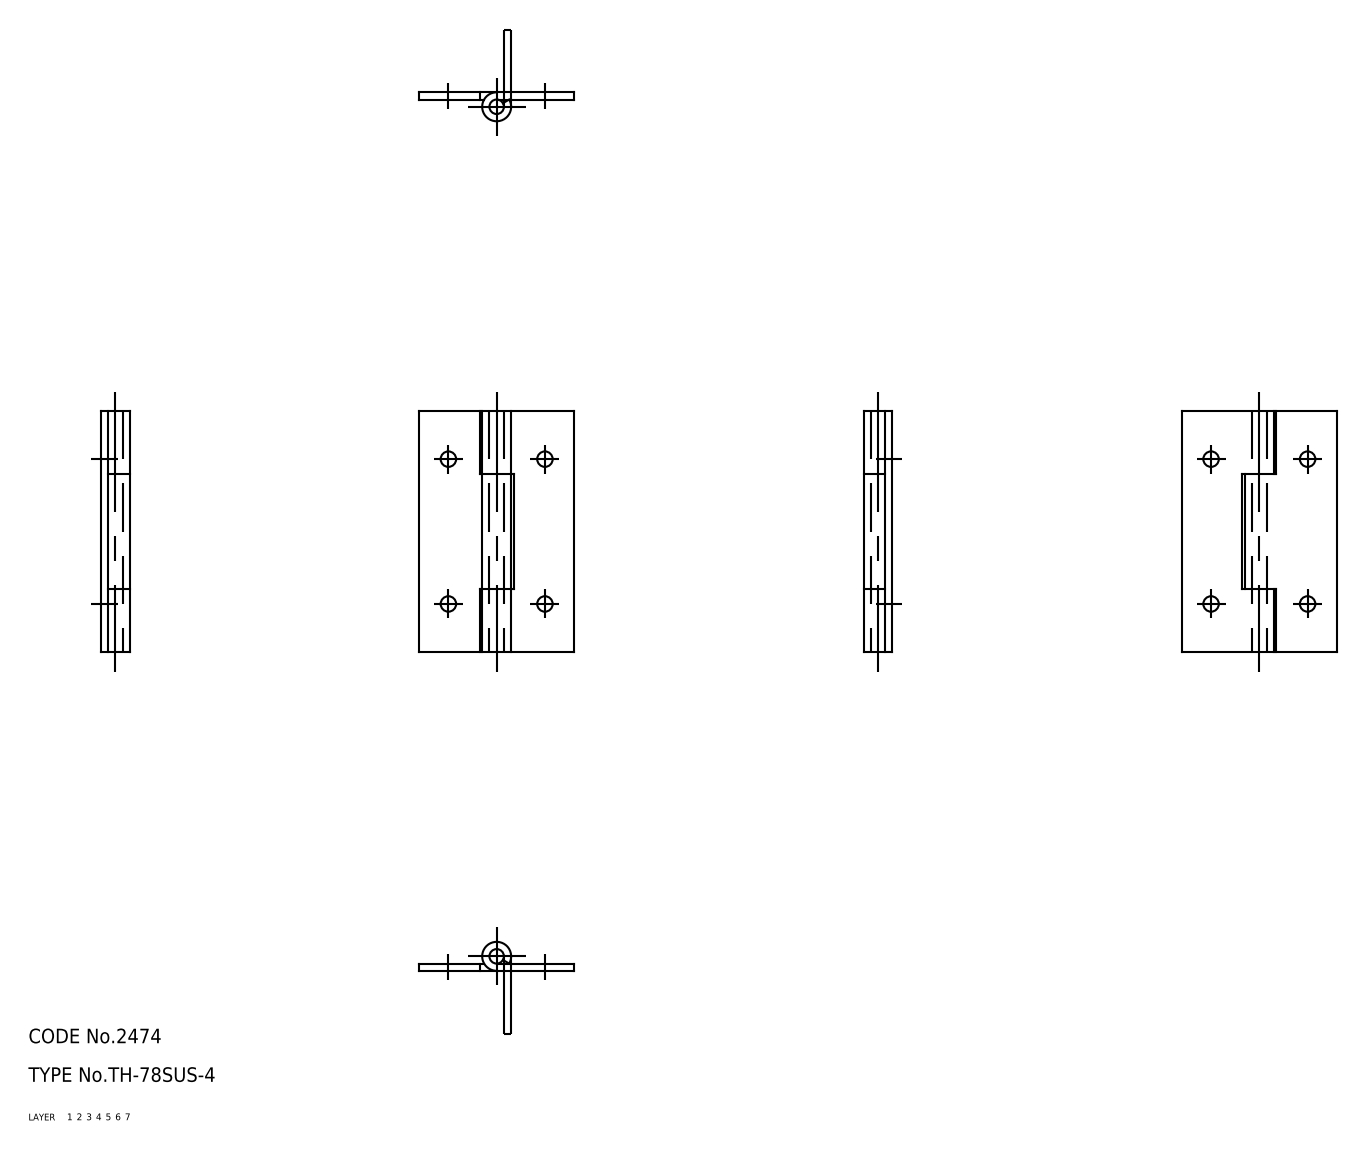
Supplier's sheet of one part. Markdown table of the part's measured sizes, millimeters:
| quantity | value |
| --- | --- |
| part name | hinge piece_B; hinge piece_A; shaft; TH_78SUS_4_17245_36 |
| STEP written by | CADfix (AUTOMOTIVE_DESIGN) |
| units | millimeters |
| bodies | 3 solids, 38 faces (0 planar, 0 cylindrical, 38 other) |
| overall size | 50 × 32 × 6 |
| volume | 3 324 mm³ |
| surface area | 5 018 mm² |
